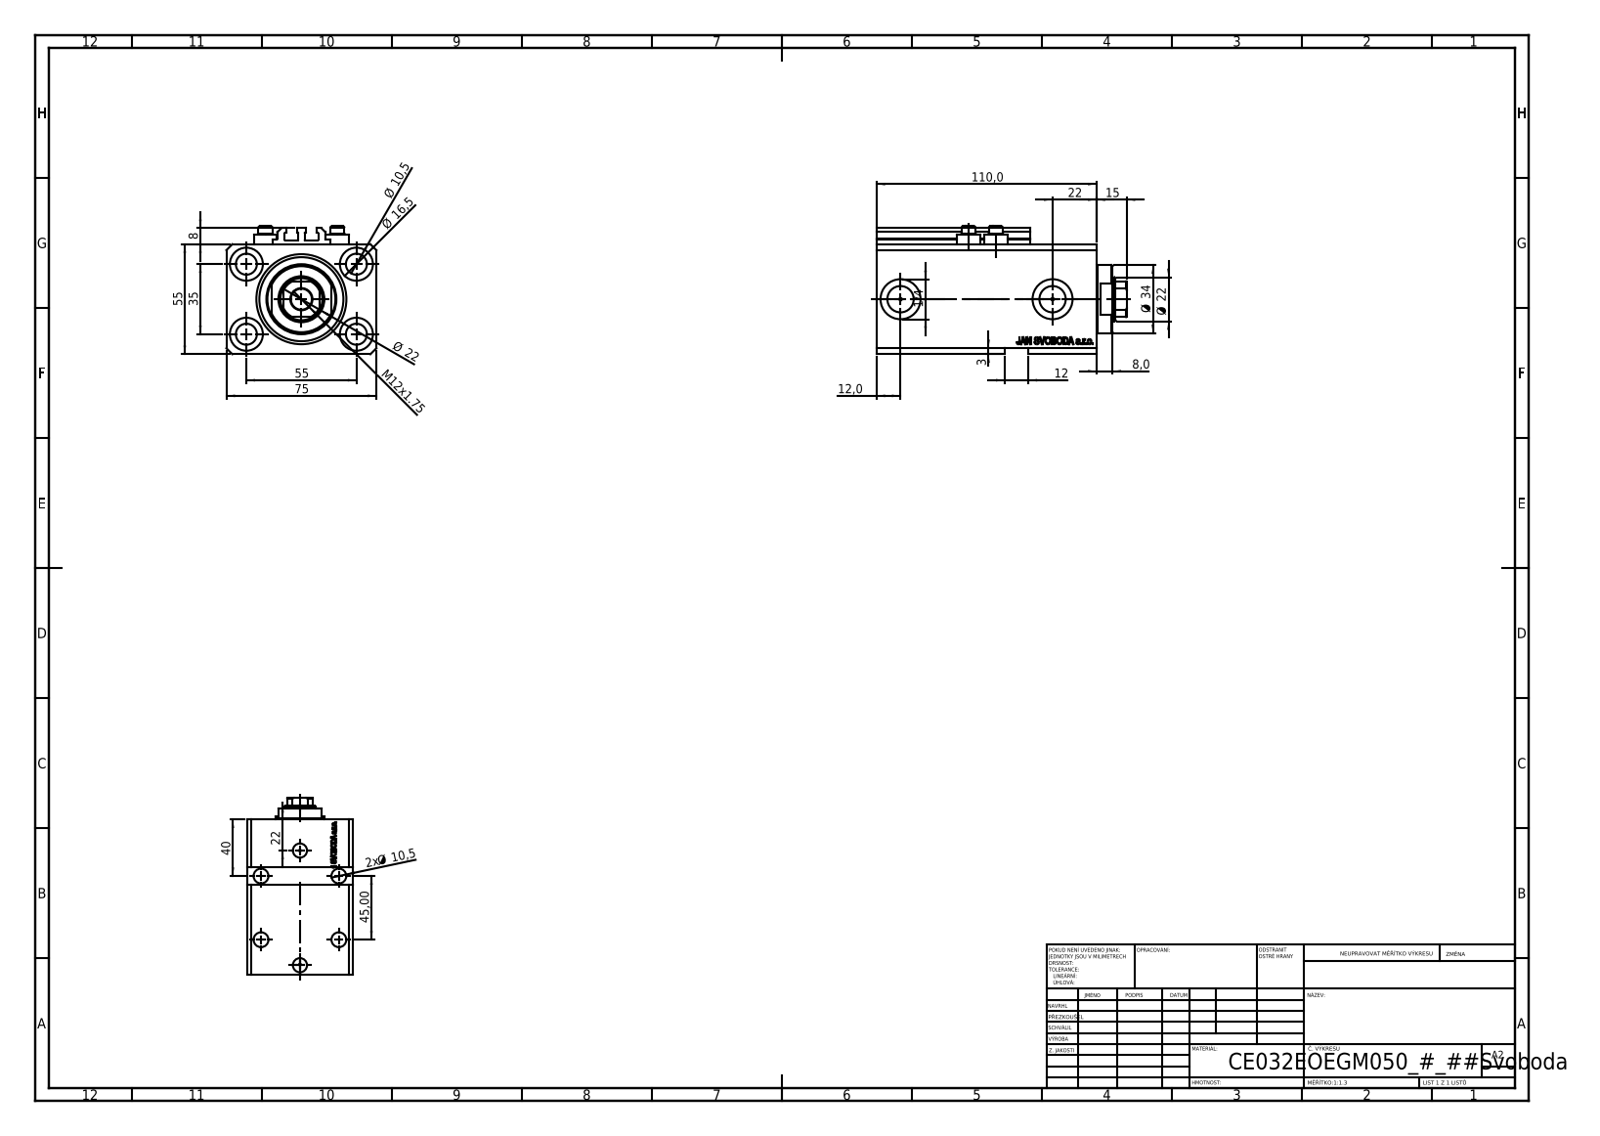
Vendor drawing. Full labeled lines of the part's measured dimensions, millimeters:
Part name (STEP PRODUCT): V250CE_VC_E; V250CE_E_Body; V250CE_C_VCP; ALLEN BOLT V250CE
STEP written by: SolidWorks 2019 (CONFIG_CONTROL_DESIGN)
Units: millimetres
Bodies: 8 solids, 1084 faces (514 planar, 146 cylindrical, 424 other)
Overall size (bounding box): 125 × 75 × 64
Volume: 381 338 mm³ · Surface area: 95 642 mm²
Round holes (diameter × count): ⌀10.5 ×9, ⌀1.25 ×4, ⌀4 ×4, ⌀16.5 ×4, ⌀10 ×2, ⌀13.16 ×2, ⌀20 ×2, ⌀22 ×1, ⌀32 ×1, ⌀45 ×1
Round bosses / shafts (diameter × count): ⌀11.6 ×4, ⌀7 ×4, ⌀34 ×1
Partial cylindrical surfaces — rounded edges, fillets, slot ends (radius × count): R0.2 ×10, R10.5 ×1
Main face-to-face distances: 55, 75, 15, 110, 95, 3, 9.9, 85.1, 100.1, 57
Hole centre spacings: 32.6, 32.87, 55, 68.74, 13.6, 14.09, 23.05, 25.81
